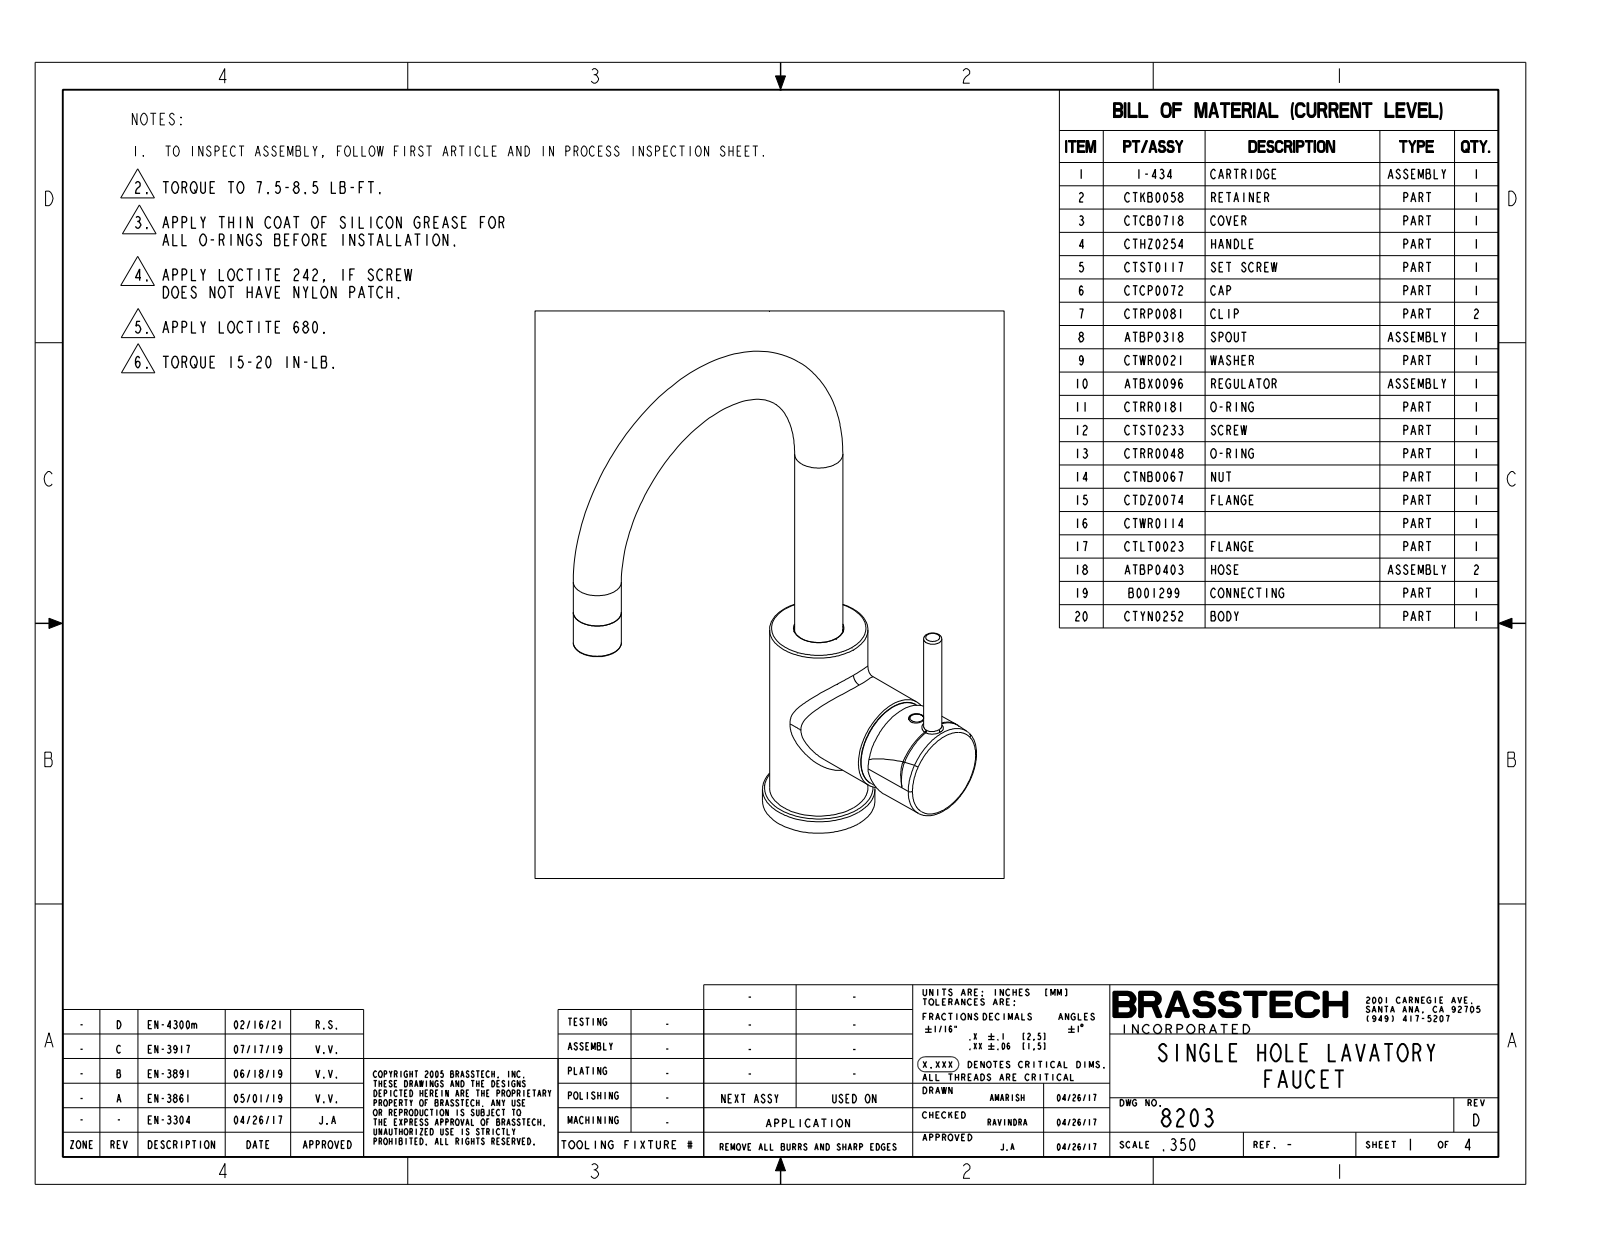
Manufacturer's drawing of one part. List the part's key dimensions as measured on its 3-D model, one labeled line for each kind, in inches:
Part name (STEP PRODUCT): 8203_SW0001
STEP written by: CREO PARAMETRIC BY PTC INC, 2018400 (AUTOMOTIVE_DESIGN)
Units: inches
Bodies: 1 solid, 236 faces (38 planar, 76 cylindrical, 122 other)
Overall size (bounding box): 11.882 × 7.717 × 4.579
Volume: 19.88 in³ · Surface area: 154.7 in²
Round holes (diameter × count): ⌀0.85 ×2, ⌀0.866 ×1, ⌀1.437 ×1
Round bosses / shafts (diameter × count): ⌀0.945 ×2, ⌀2.205 ×1, ⌀1.929 ×1, ⌀1.89 ×1, ⌀1.681 ×1, ⌀0.827 ×1, ⌀0.354 ×1, ⌀0.315 ×1
Partial cylindrical surfaces — rounded edges, fillets, slot ends (radius × count): R0.039 ×24, R0.079 ×8, R0.02 ×7
Main face-to-face distances: 4.154, 1.272, 1.22, 0.051, 6.862, 2.709, 0.315, 3.839, 6.547, 7.737
Hole centre spacings: 6.142
